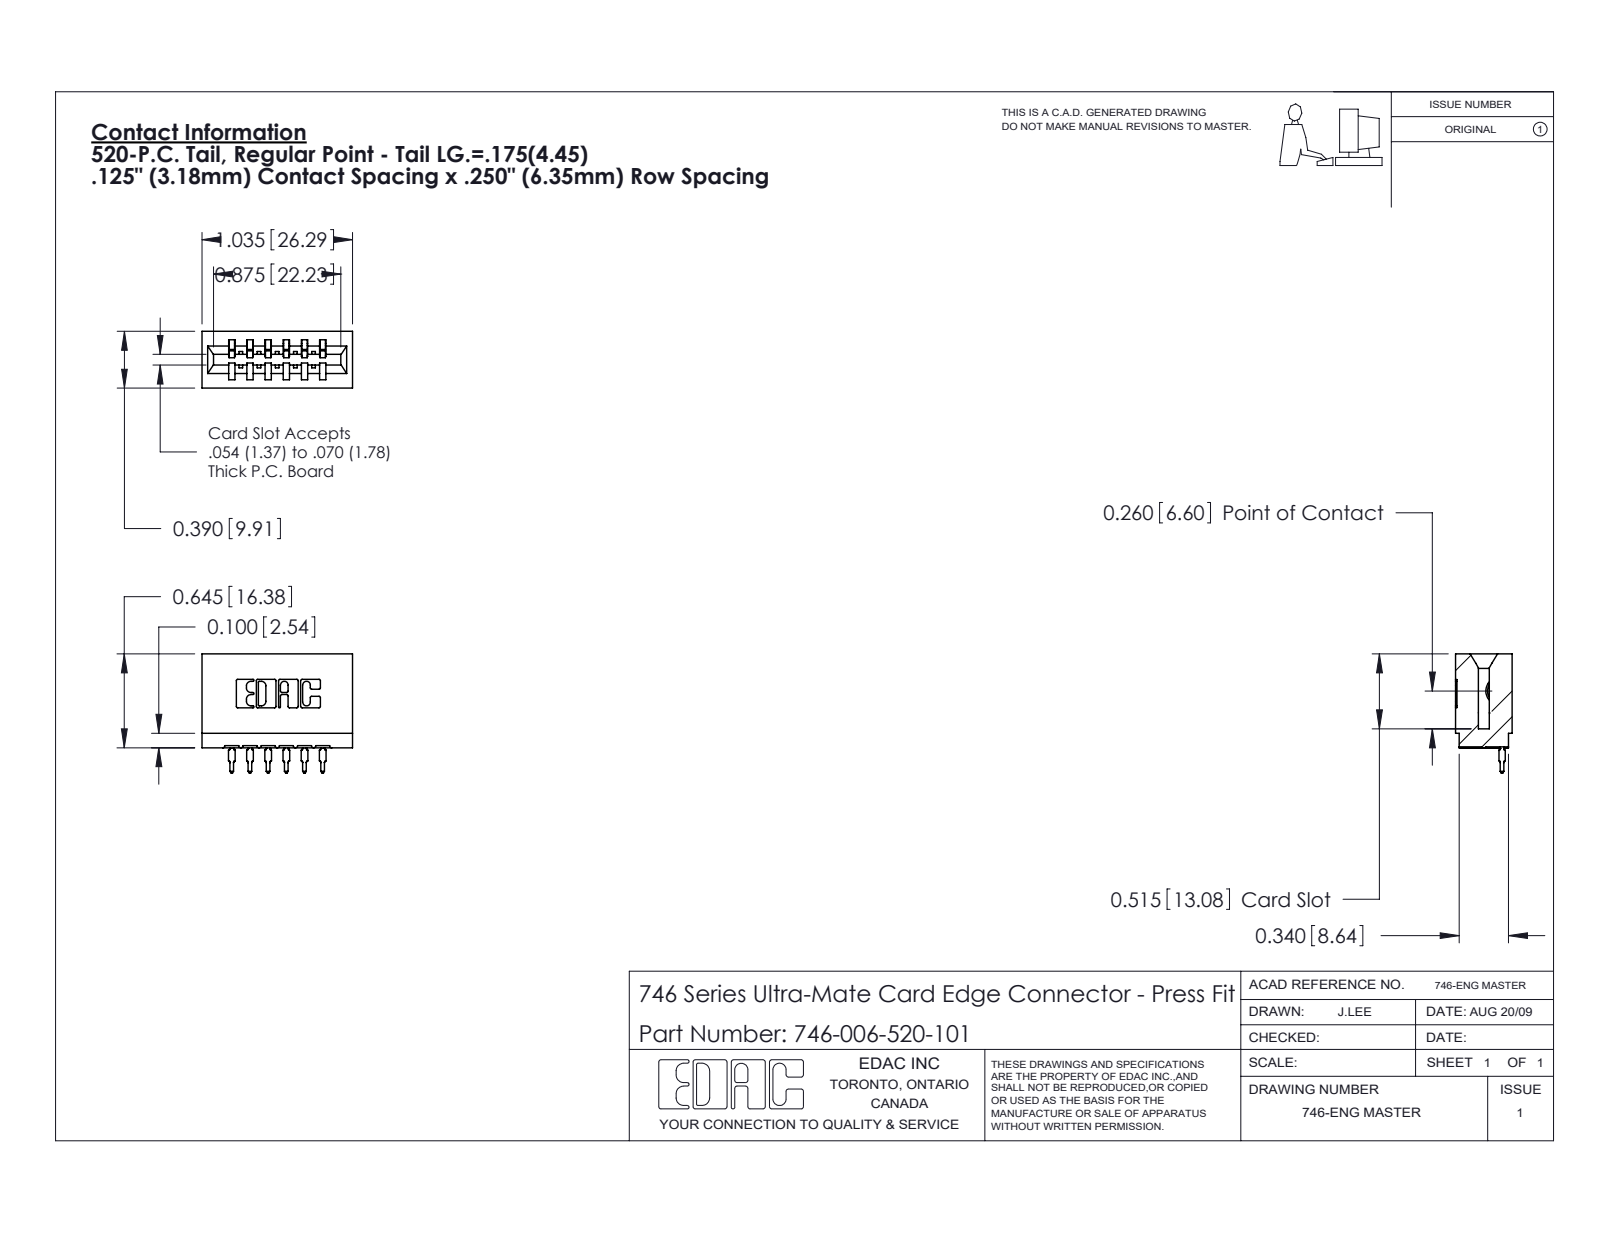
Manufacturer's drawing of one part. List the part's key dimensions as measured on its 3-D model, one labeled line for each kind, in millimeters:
Part name (STEP PRODUCT): 746 Part_.515 Slot Depth - 01; 746-006-520-101; 746-292-001_520
STEP written by: SolidWorks 2020 (CONFIG_CONTROL_DESIGN)
Units: millimetres
Bodies: 7 solids, 745 faces (433 planar, 156 cylindrical, 156 other)
Overall size (bounding box): 26.3 × 20.8 × 9.9
Volume: 2 980 mm³ · Surface area: 3 774 mm²
Partial cylindrical surfaces — rounded edges, fillets, slot ends (radius × count): R0.3 ×22, R0.5 ×12, R0.4 ×7, R0.2 ×6, R0.8 ×6, R0.1 ×4, R0.3 ×4, R0.7 ×3
Main face-to-face distances: 6.4, 3.2, 1.1, 8.5, 1.4, 3.2, 9.9, 7.4, 5.3, 9.5
